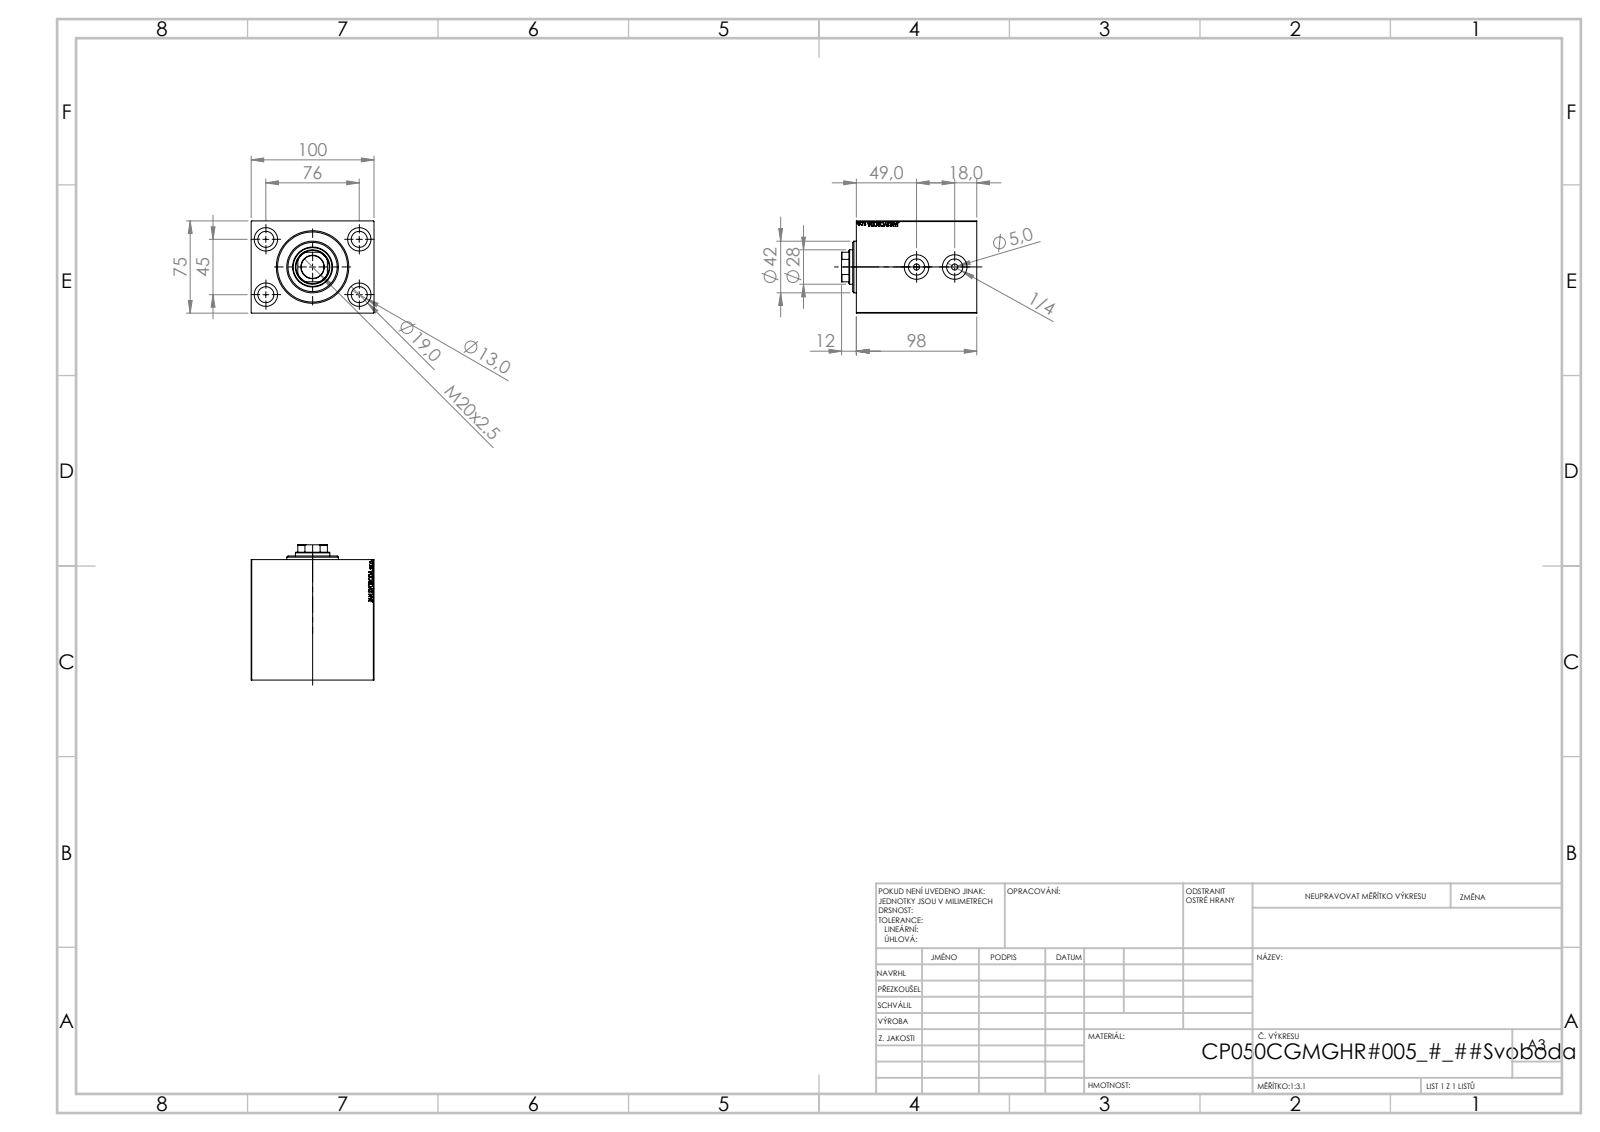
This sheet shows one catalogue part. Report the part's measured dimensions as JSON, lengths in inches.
{"part_name": "V450CP_B_VCP; V450CP_C; V450CP_VC_B", "step_written_by": "SolidWorks 2019 (CONFIG_CONTROL_DESIGN)", "units": "inches", "bodies": {"solids": 3, "faces": 888, "planar": 414, "cylindrical": 76, "other": 398}, "overall_size": [4.331, 3.937, 2.953], "volume_in3": 40.06, "surface_area_in2": 177.3, "round_holes": [[0.512, 4], [0.748, 4], [0.157, 2], [0.197, 2], [0.383, 2], [0.518, 2], [0.591, 2], [0.787, 2], [0.728, 1], [1.102, 1], [1.24, 1], [1.28, 1]], "round_bosses_or_shafts": [[1.654, 1]], "partial_cylinders_radius": [[0.531, 1]], "face_to_face_distances": [2.953, 3.937, 3.858, 1.929, 0.551, 3.307, 1.732, 0.197, 1.378, 1.181], "hole_center_spacings": [1.739, 1.772, 2.992, 3.477, 1.22, 1.675]}
